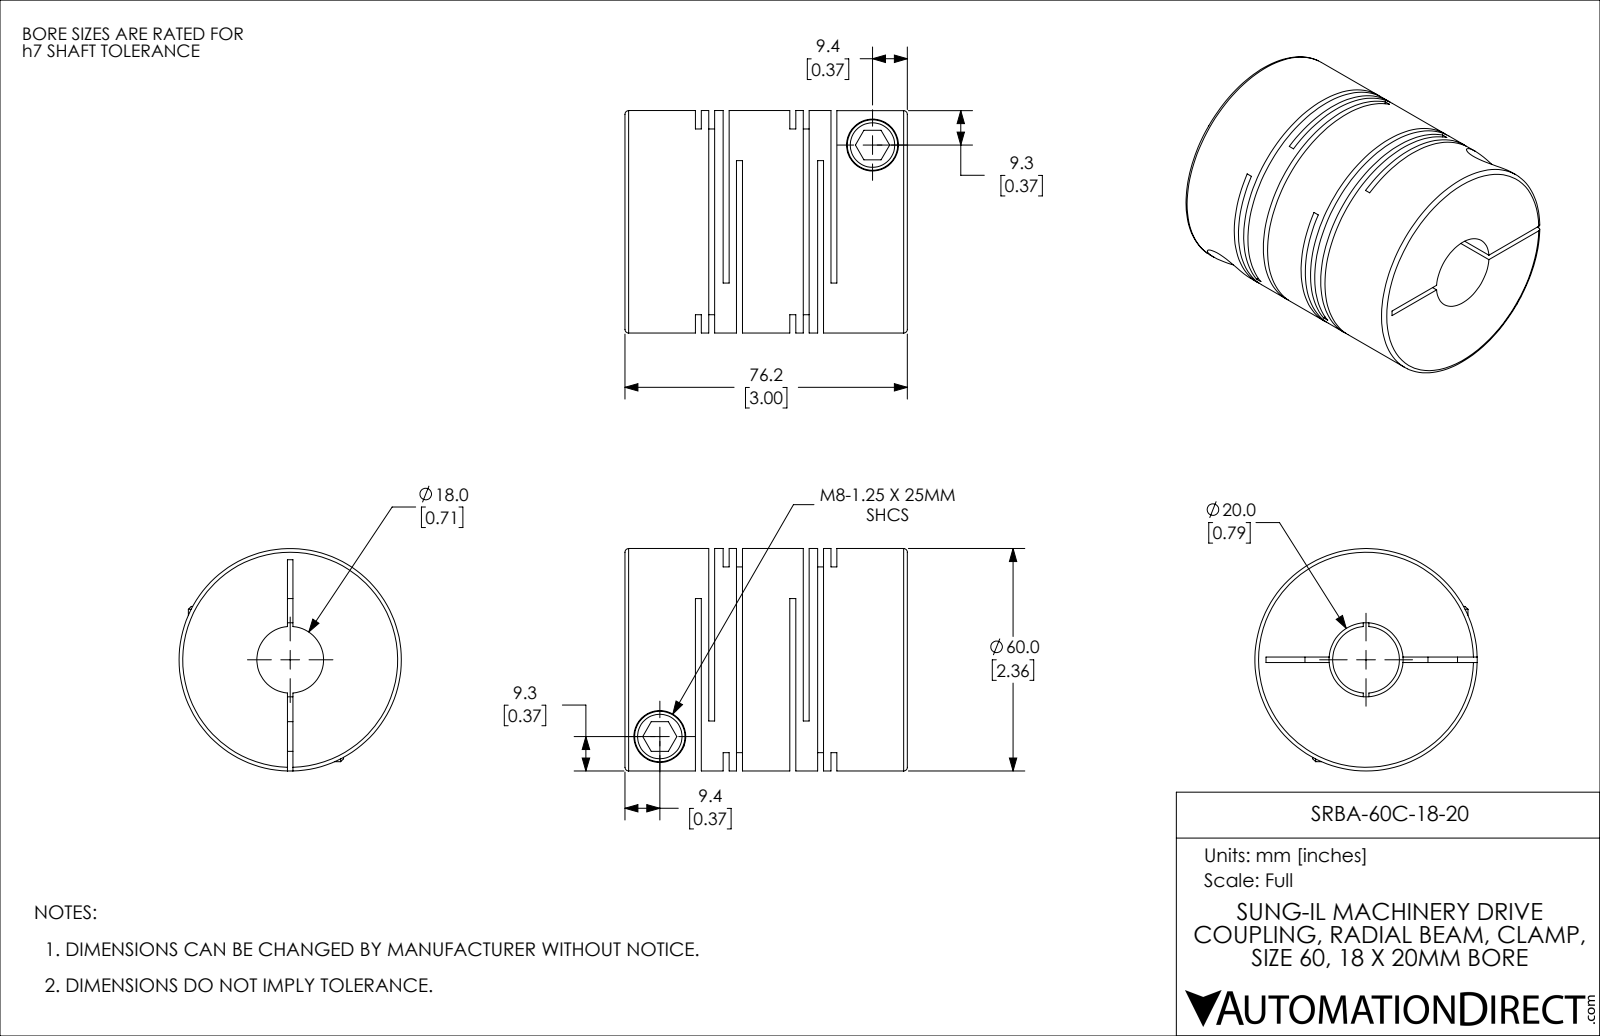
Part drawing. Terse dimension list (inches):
name: SRBA-60C-18-20
written by: SolidWorks 2021 (CONFIG_CONTROL_DESIGN)
unit: in
bodies: 1 solid, 115 faces (60 planar, 42 cylindrical, 13 other)
size: 3 × 2.362 × 2.362
volume: 9.847 in³; area: 91.75 in²
holes: 2× ⌀0.315, 2× ⌀0.551, 1× ⌀0.709, 1× ⌀0.787
bosses: 2× ⌀0.535, 1× ⌀2.362
face distances: 0.063, 0.142, 0.295, 1.004, 1.299, 1.067, 0.232, 0.941, 0.709, 0.079
